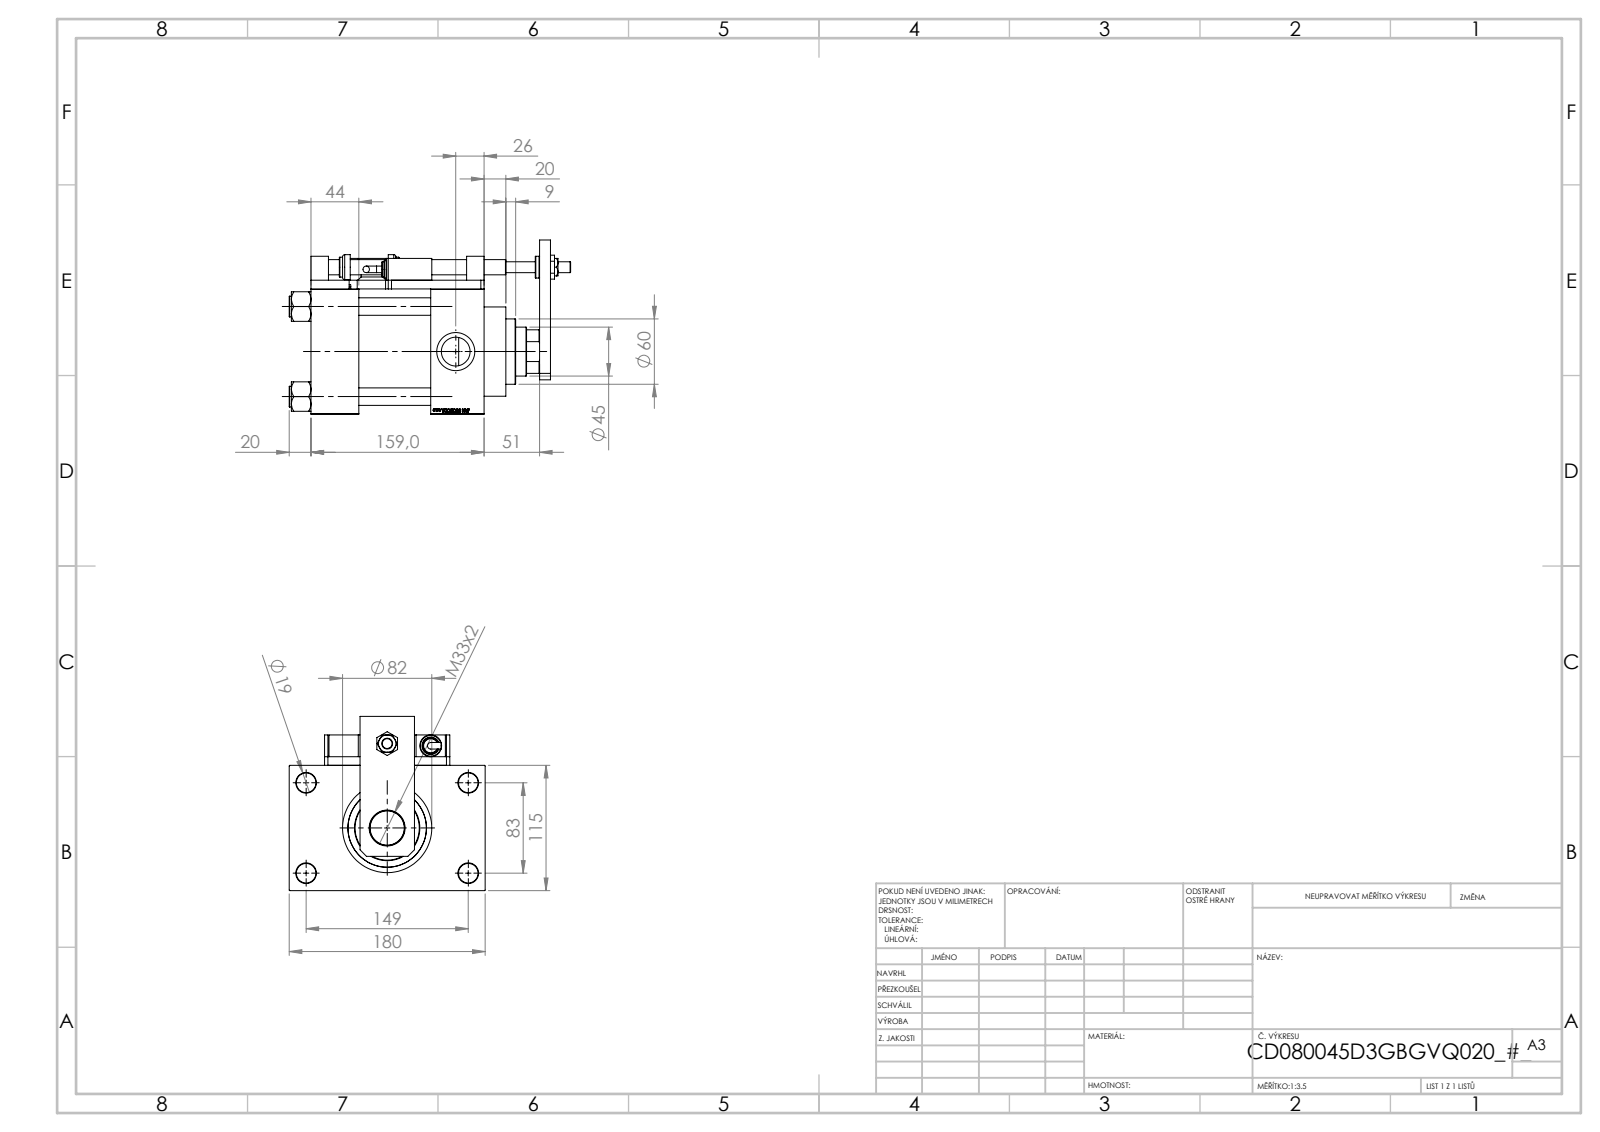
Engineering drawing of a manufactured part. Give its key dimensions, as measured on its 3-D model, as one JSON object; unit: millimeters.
{"part_name": "V215CD_SWITCH_Q_BLOK; Zatka_pro_OIL_PORT; V215CD_SWITCH_Q_PODLOZKA_FRONT; V215CD_NUT_M5_D (+7 more)", "step_written_by": "SolidWorks 2019 (CONFIG_CONTROL_DESIGN)", "units": "millimeters", "bodies": {"solids": 26, "faces": 1480, "planar": 714, "cylindrical": 167, "other": 599}, "overall_size": [258.5, 180, 160], "volume_mm3": 2282000, "surface_area_mm2": 399868, "round_holes": [[8.5, 4], [13.5, 4], [16, 4], [18, 4], [26.44, 4], [35, 4], [7, 3], [10, 1], [14, 1], [31.5, 1], [33, 1], [45, 1]], "round_bosses_or_shafts": [[19, 4], [20, 3], [16, 2], [14, 2], [6, 2], [86, 1], [82, 1], [60, 1]], "partial_cylinders_radius": [[7.5, 4], [22, 1]], "face_to_face_distances": [115, 110, 8, 66, 49, 44, 123, 159, 32.5, 20], "hole_center_spacings": [33.15, 58.48, 82.7, 85.28, 89.24, 115.85, 142.43, 21.26]}
